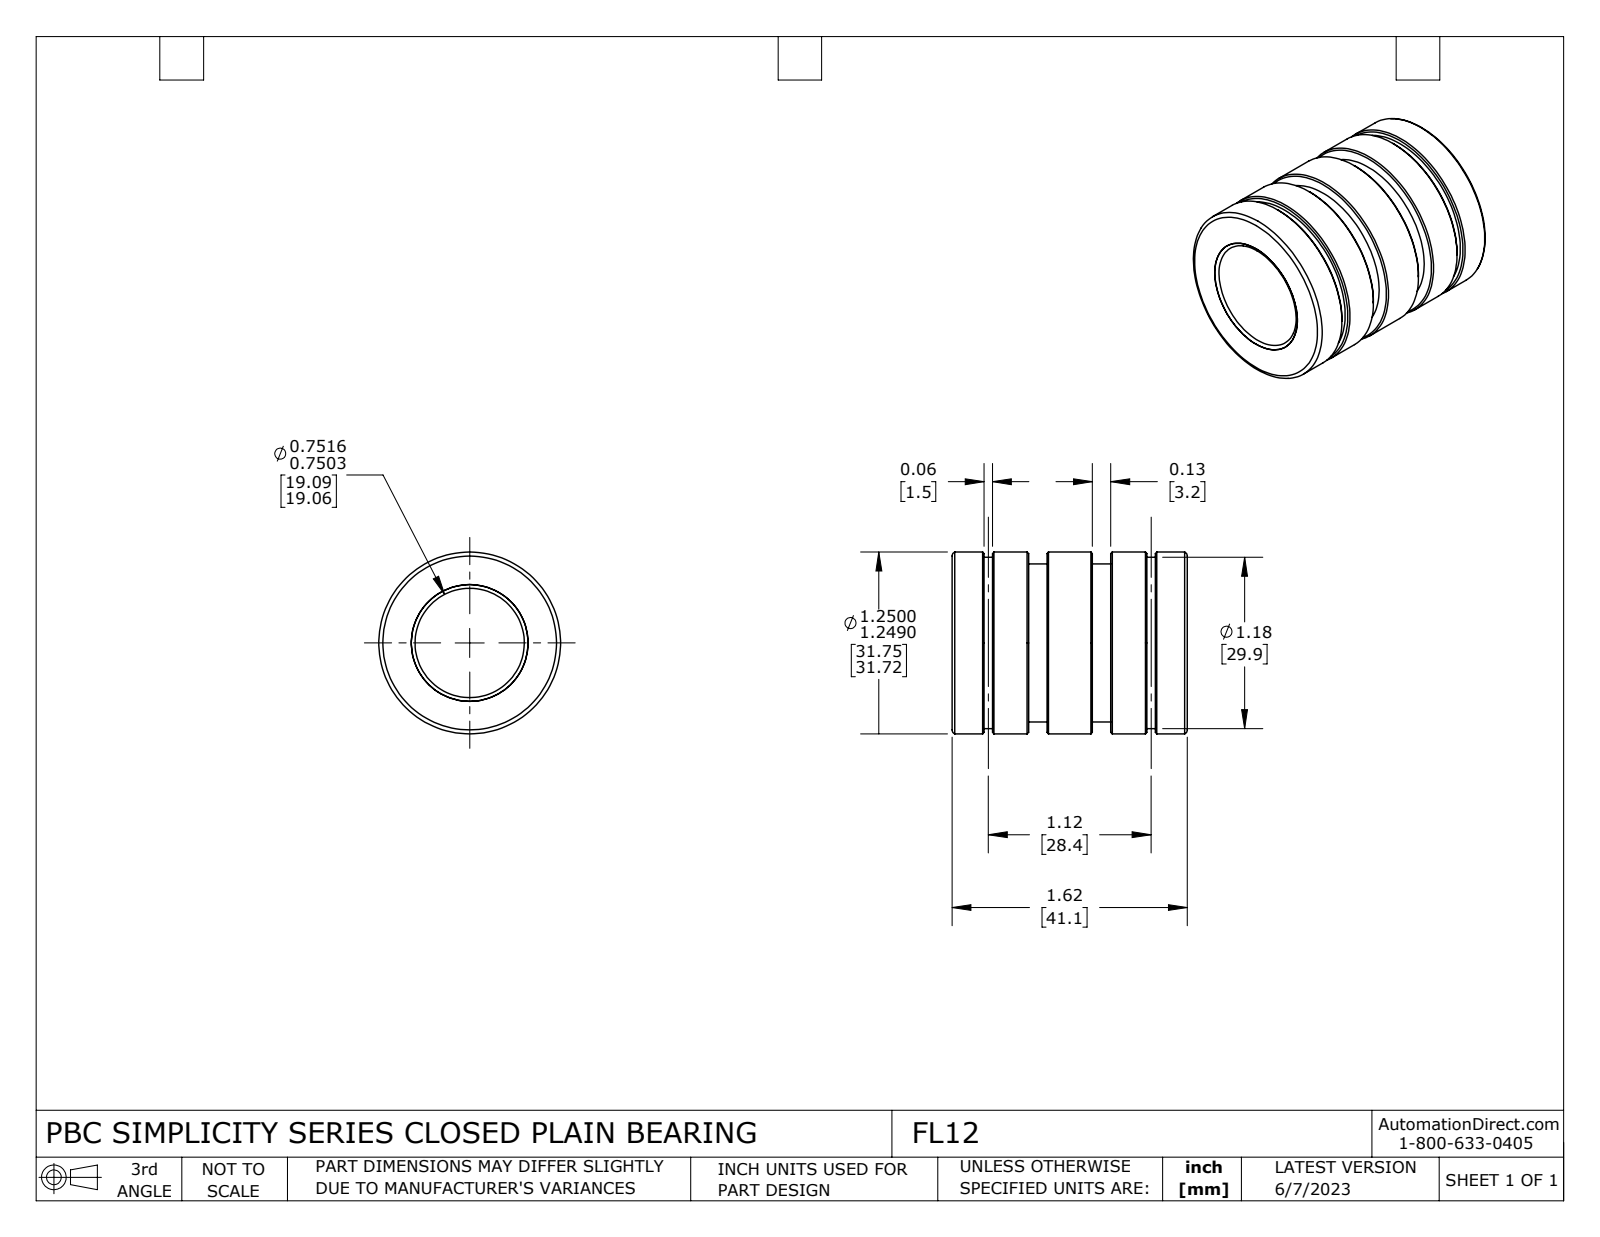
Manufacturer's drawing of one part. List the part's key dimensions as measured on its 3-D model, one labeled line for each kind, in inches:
Part name (STEP PRODUCT): FL12
STEP written by: SolidWorks 2021 (CONFIG_CONTROL_DESIGN)
Units: inches
Bodies: 2 solids, 58 faces (10 planar, 24 cylindrical, 24 other)
Overall size (bounding box): 1.618 × 1.249 × 1.249
Volume: 1.171 in³ · Surface area: 21.14 in²
Round holes (diameter × count): ⌀0.751 ×1, ⌀0.802 ×1
Round bosses / shafts (diameter × count): ⌀1.249 ×1, ⌀1.177 ×1, ⌀1.087 ×1
Main face-to-face distances: 1.617, 0.527, 1.091, 0.653, 0.965, 0.126, 0.438, 0.564, 0.312, 0.278
